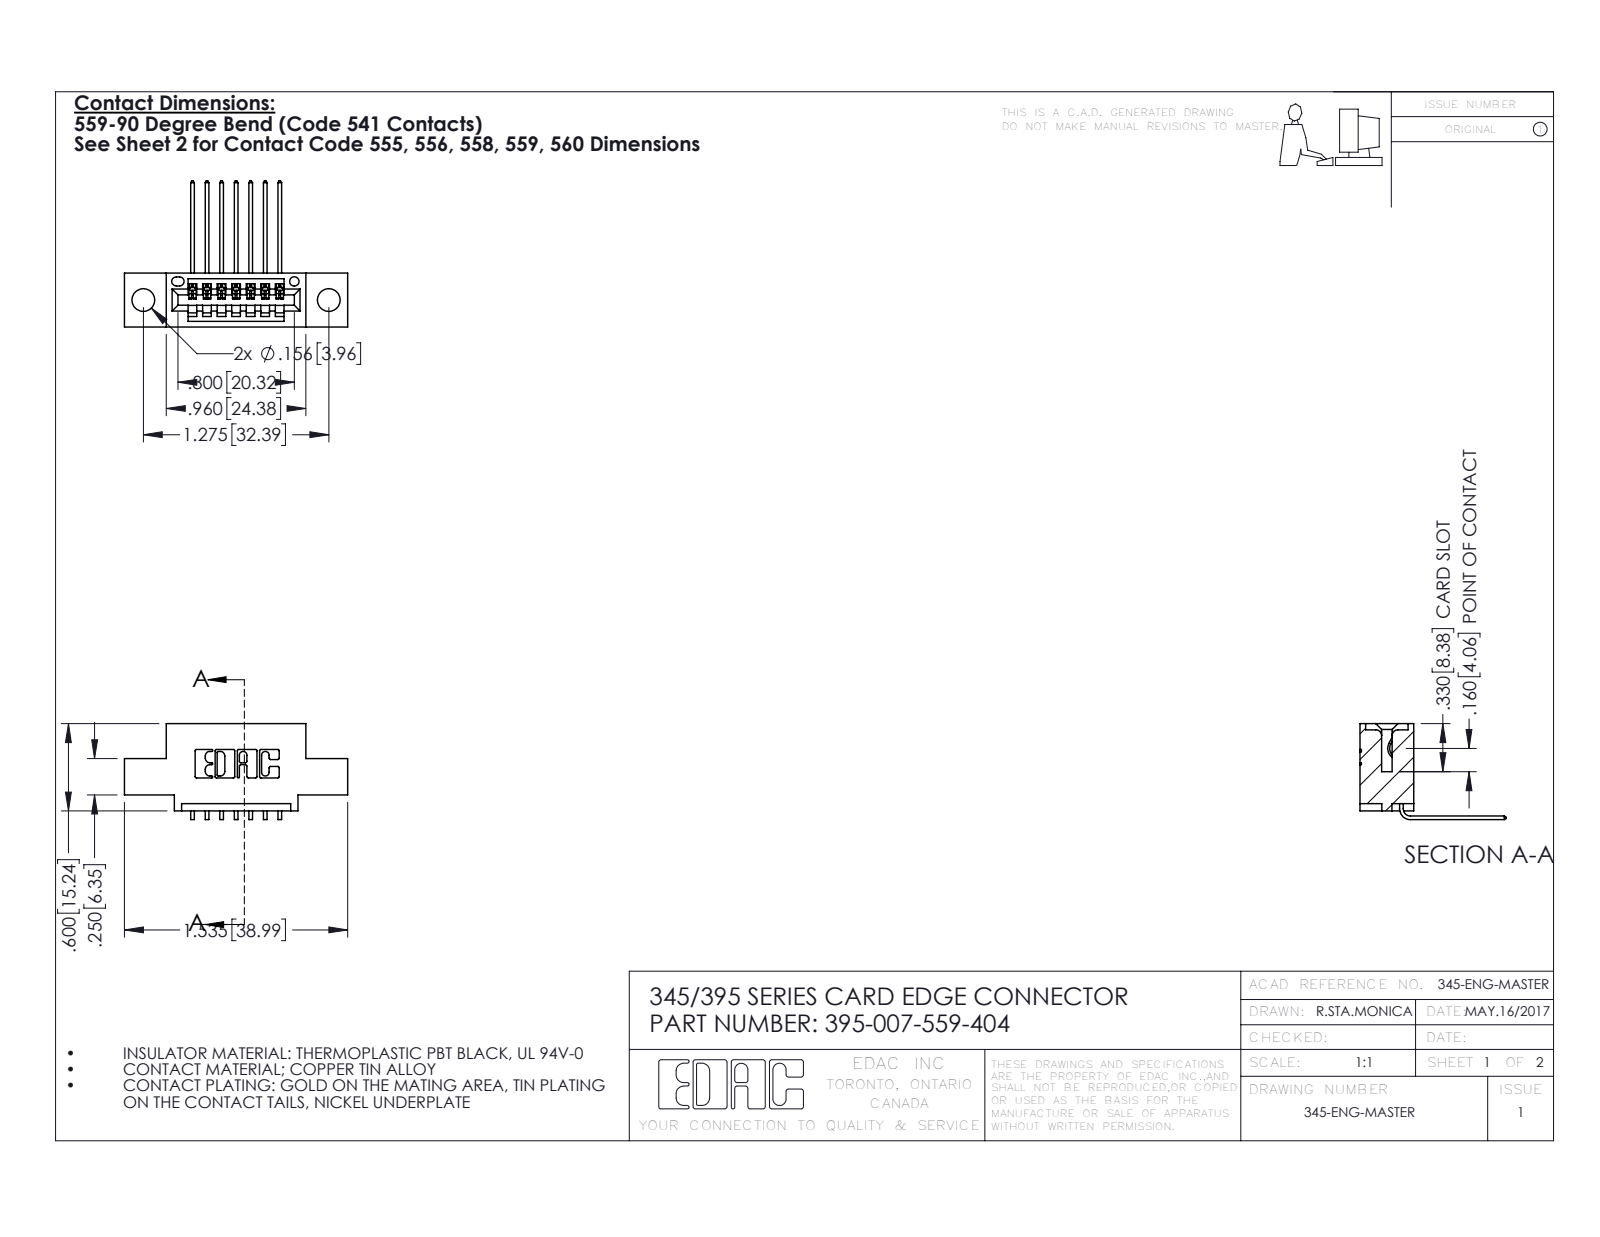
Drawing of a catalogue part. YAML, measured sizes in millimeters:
part_name: "345-292-001_558 559 Tail - 1; 395-007-559-404; 345 Part_0.110 Offset - 0.156 Dia-TH"
step_written_by: "SolidWorks 2016 (CONFIG_CONTROL_DESIGN)"
units: millimeters
bodies: {solids: 8, faces: 550, planar: 378, cylindrical: 172, other: 0}
overall_size: [39, 25.5, 16.7]
volume: 3280
surface_area: 3909
round_holes:
  - {diameter: 4, count: 2}
  - {diameter: 1.6, count: 1}
partial_cylinders:
  - {radius: 0.3, count: 22}
  - {radius: 0.2, count: 14}
  - {radius: 0.2, count: 6}
  - {radius: 0.8, count: 6}
  - {radius: 0.7, count: 3}
  - {radius: 0.8, count: 2}
  - {radius: 1, count: 2}
  - {radius: 0.4, count: 1}
face_to_face_distances: [5.1, 9.4, 2.5, 1.8, 7.6, 7.6, 4.1, 1.5, 2.5, 6.9]
hole_center_spacings: [6.9, 26.5, 32.4]
